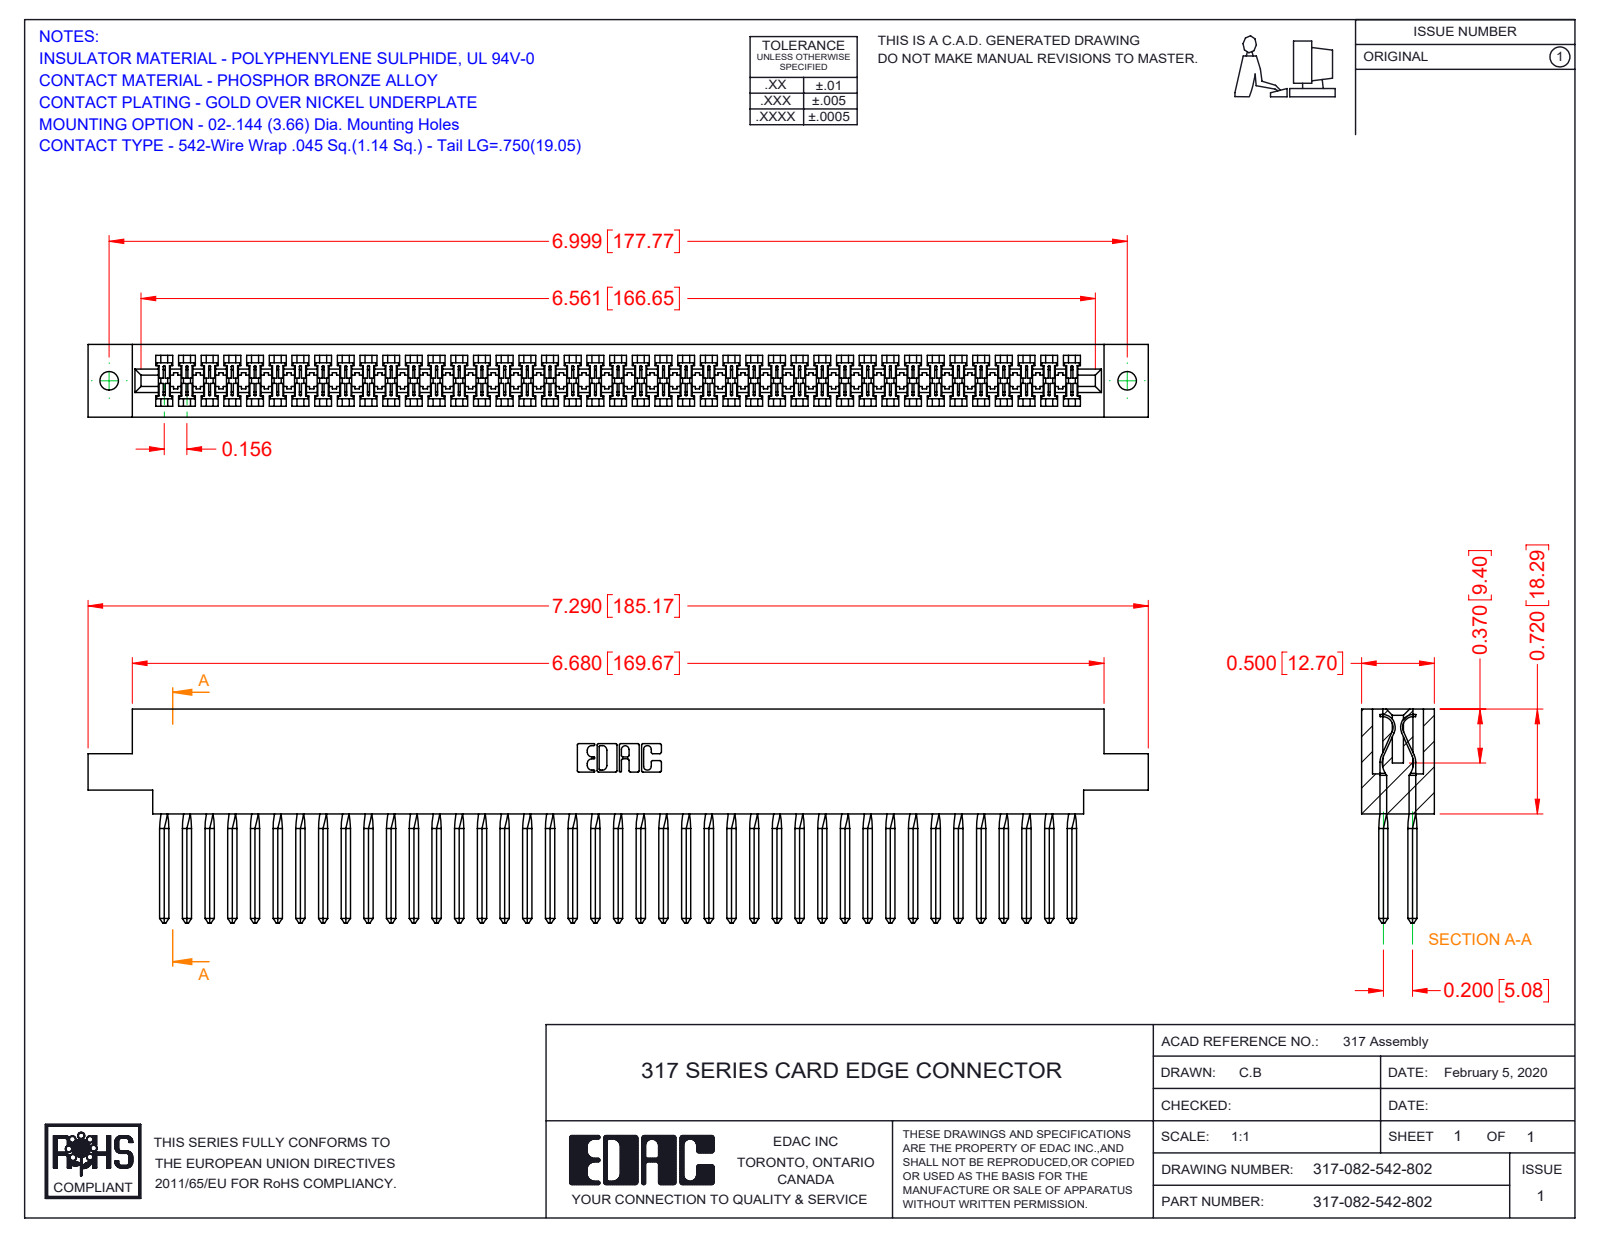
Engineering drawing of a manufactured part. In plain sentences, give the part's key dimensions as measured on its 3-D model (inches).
The part is named "317-290-003_542; 317 Part_.144 Dia; 317-082-542-802". Its 3-D file was written by "SolidWorks 2016 (CONFIG_CONTROL_DESIGN)". It is 83 solids with 4776 faces: 3830 planar, 618 cylindrical and 328 other. Overall it measures 7.29 by 1.47 by 0.5 inches. Its volume is 1.846 cubic inches and its surface area 64.74 square inches. Round holes: 2 of diameter 0.128. Partial cylindrical surfaces (rounded edges, fillets, slot ends): 164 of radius 0.006, 22 of radius 0.01, 6 of radius 0.007, 6 of radius 0.031, 3 of radius 0.026, 2 of radius 0.074, 2 of radius 0.089, 2 of radius 0.1. The main face-to-face distances are 0.5, 0.075, 0.425, 0.35, 0.2, 0.046, 0.128, 0.372, 0.052, 0.297. The hole center spacings are 6.999.
